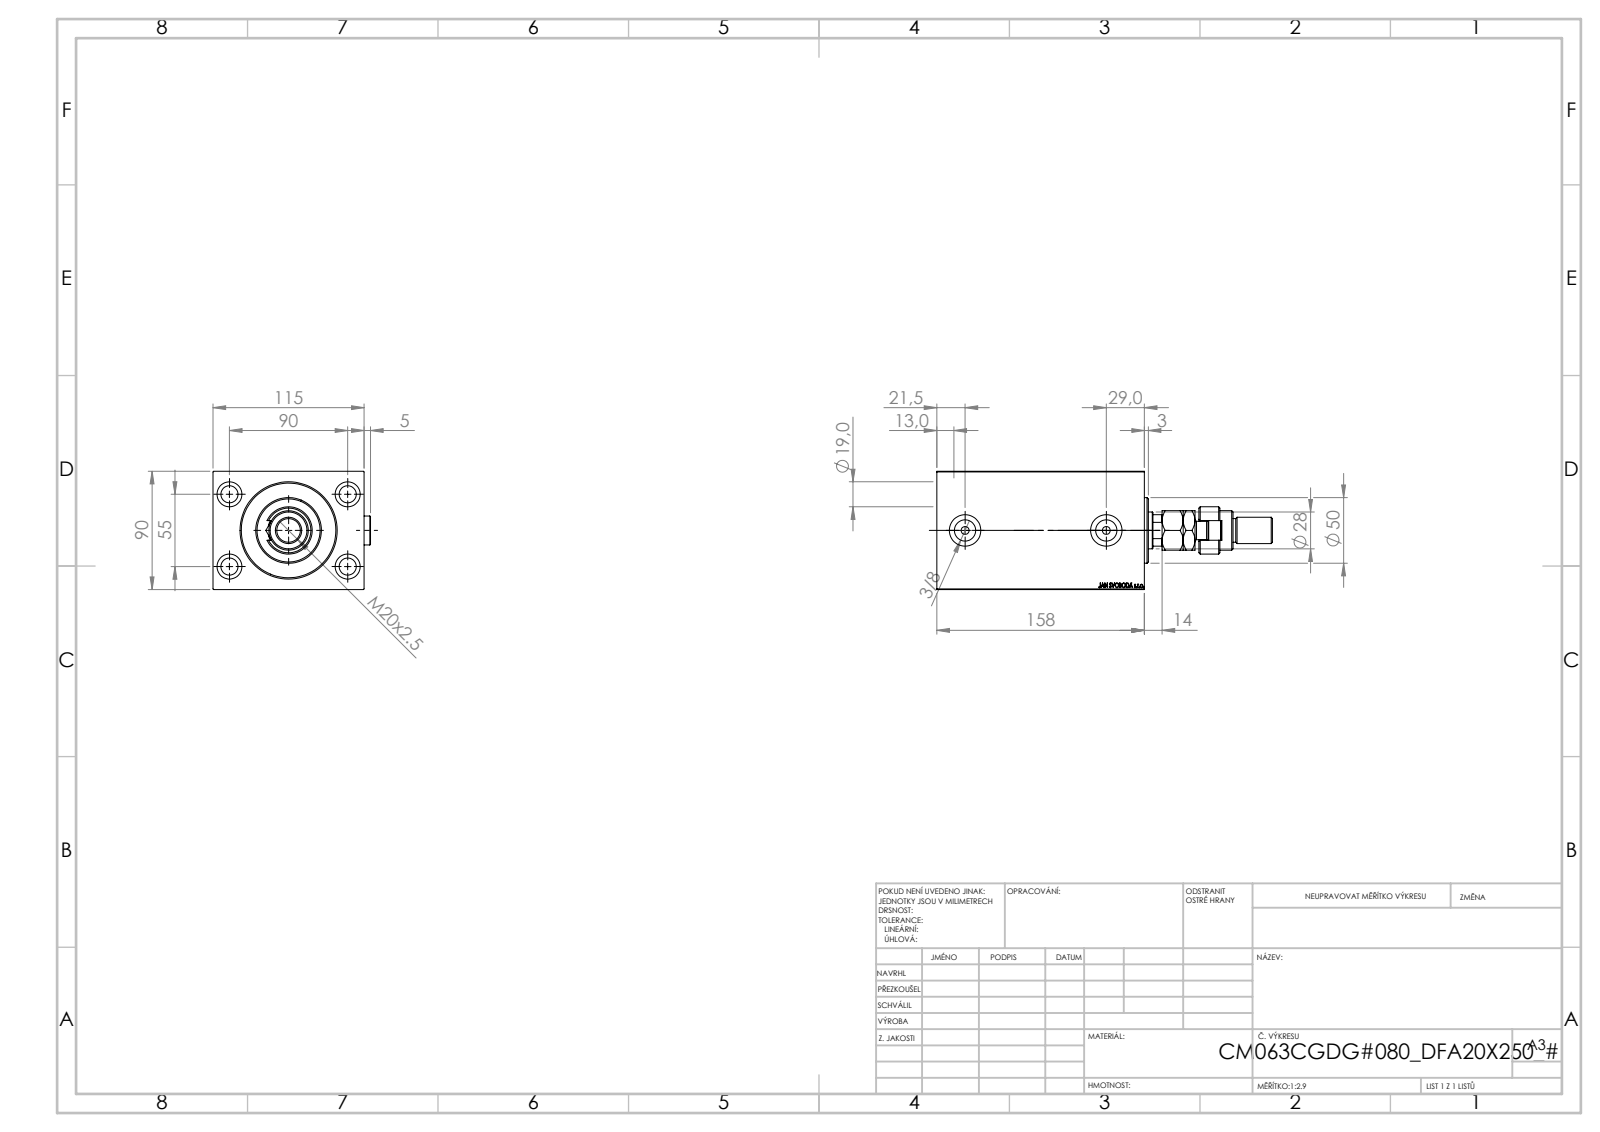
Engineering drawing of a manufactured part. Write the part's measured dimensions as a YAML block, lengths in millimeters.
part_name: "V450CM_VC_B; MFA; Zatka_OIL_PORT; V450CM_C_Body (+2 more)"
step_written_by: "SolidWorks 2019 (CONFIG_CONTROL_DESIGN)"
units: millimeters
bodies: {solids: 7, faces: 1004, planar: 471, cylindrical: 91, other: 442}
overall_size: [255.5, 119.9, 90]
volume: 1380000
surface_area: 196998
round_holes:
  - {diameter: 13, count: 4}
  - {diameter: 19, count: 4}
  - {diameter: 6, count: 2}
  - {diameter: 16.17, count: 2}
  - {diameter: 24, count: 2}
  - {diameter: 18.5, count: 1}
  - {diameter: 28, count: 1}
  - {diameter: 31.5, count: 1}
  - {diameter: 63, count: 1}
  - {diameter: 65, count: 1}
  - {diameter: 72, count: 1}
round_bosses_or_shafts:
  - {diameter: 22, count: 3}
  - {diameter: 50, count: 1}
  - {diameter: 36, count: 1}
  - {diameter: 30, count: 1}
  - {diameter: 20, count: 1}
  - {diameter: 18, count: 1}
  - {diameter: 14, count: 1}
partial_cylinders:
  - {radius: 7.5, count: 1}
  - {radius: 12, count: 1}
  - {radius: 13.5, count: 1}
face_to_face_distances: [90, 115, 158, 17.5, 140.5, 13.5, 127, 144.5, 64.5, 47]
hole_center_spacings: [52.74, 55, 90, 105.48, 107.5]
